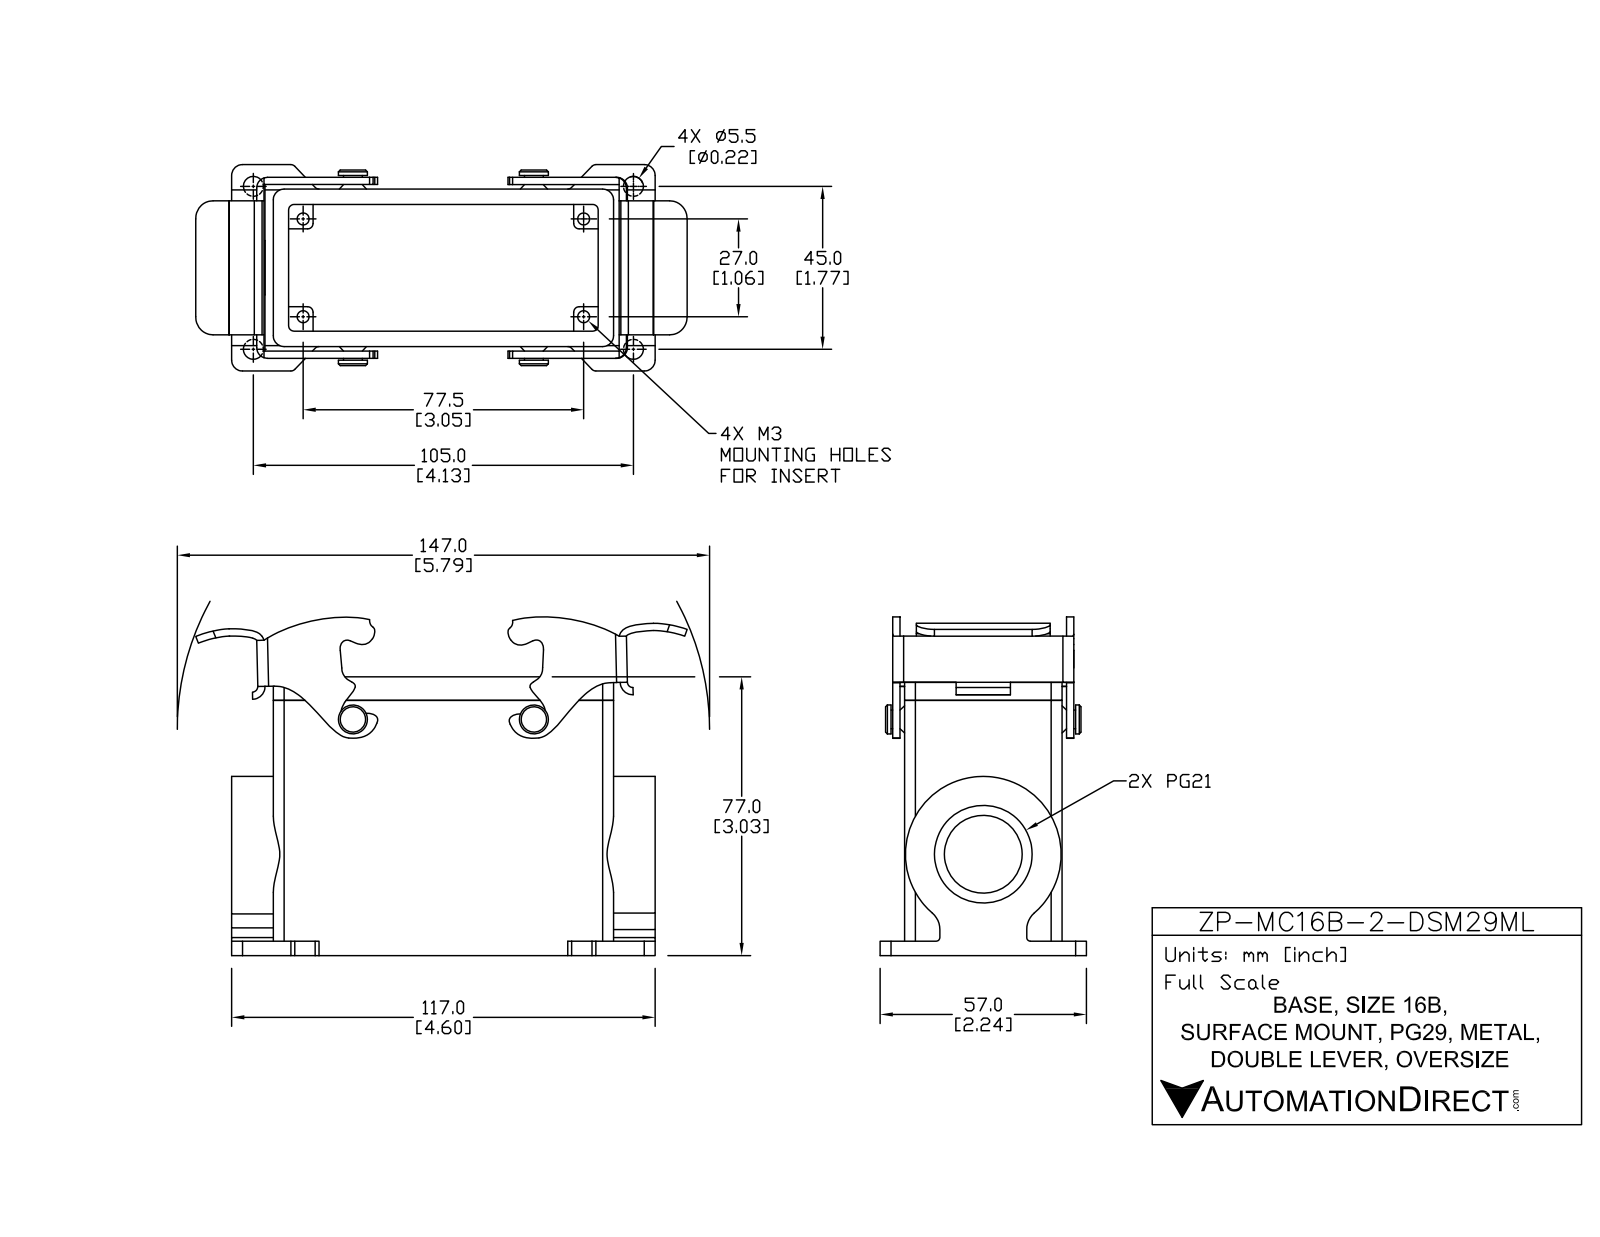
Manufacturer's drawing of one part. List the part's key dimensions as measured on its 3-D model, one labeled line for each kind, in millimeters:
Part name (STEP PRODUCT): ZP-MC16B-2-DSM29ML
STEP written by: SolidWorks 2011 (AUTOMOTIVE_DESIGN)
Units: millimetres
Bodies: 4 solids, 329 faces (135 planar, 186 cylindrical, 8 other)
Overall size (bounding box): 145.91 × 90.67 × 57
Volume: 118 506 mm³ · Surface area: 67 450 mm²
Round holes (diameter × count): ⌀3.3 ×4, ⌀5.5 ×4, ⌀30.25 ×1, ⌀35.5 ×1
Round bosses / shafts (diameter × count): ⌀8 ×2, ⌀5.17 ×2
Partial cylindrical surfaces — rounded edges, fillets, slot ends (radius × count): R0.5 ×26, R1.5 ×16, R3 ×10, R1 ×6, R2 ×6, R4 ×6, R5 ×4, R10 ×4
Main face-to-face distances: 4.25, 39.25, 43.5, 35, 2.5, 1.15, 5.5, 1.25, 40.5, 2.4
Hole centre spacings: 16.43, 38.54, 91.69, 98.09, 27, 45, 77.5, 82.07
